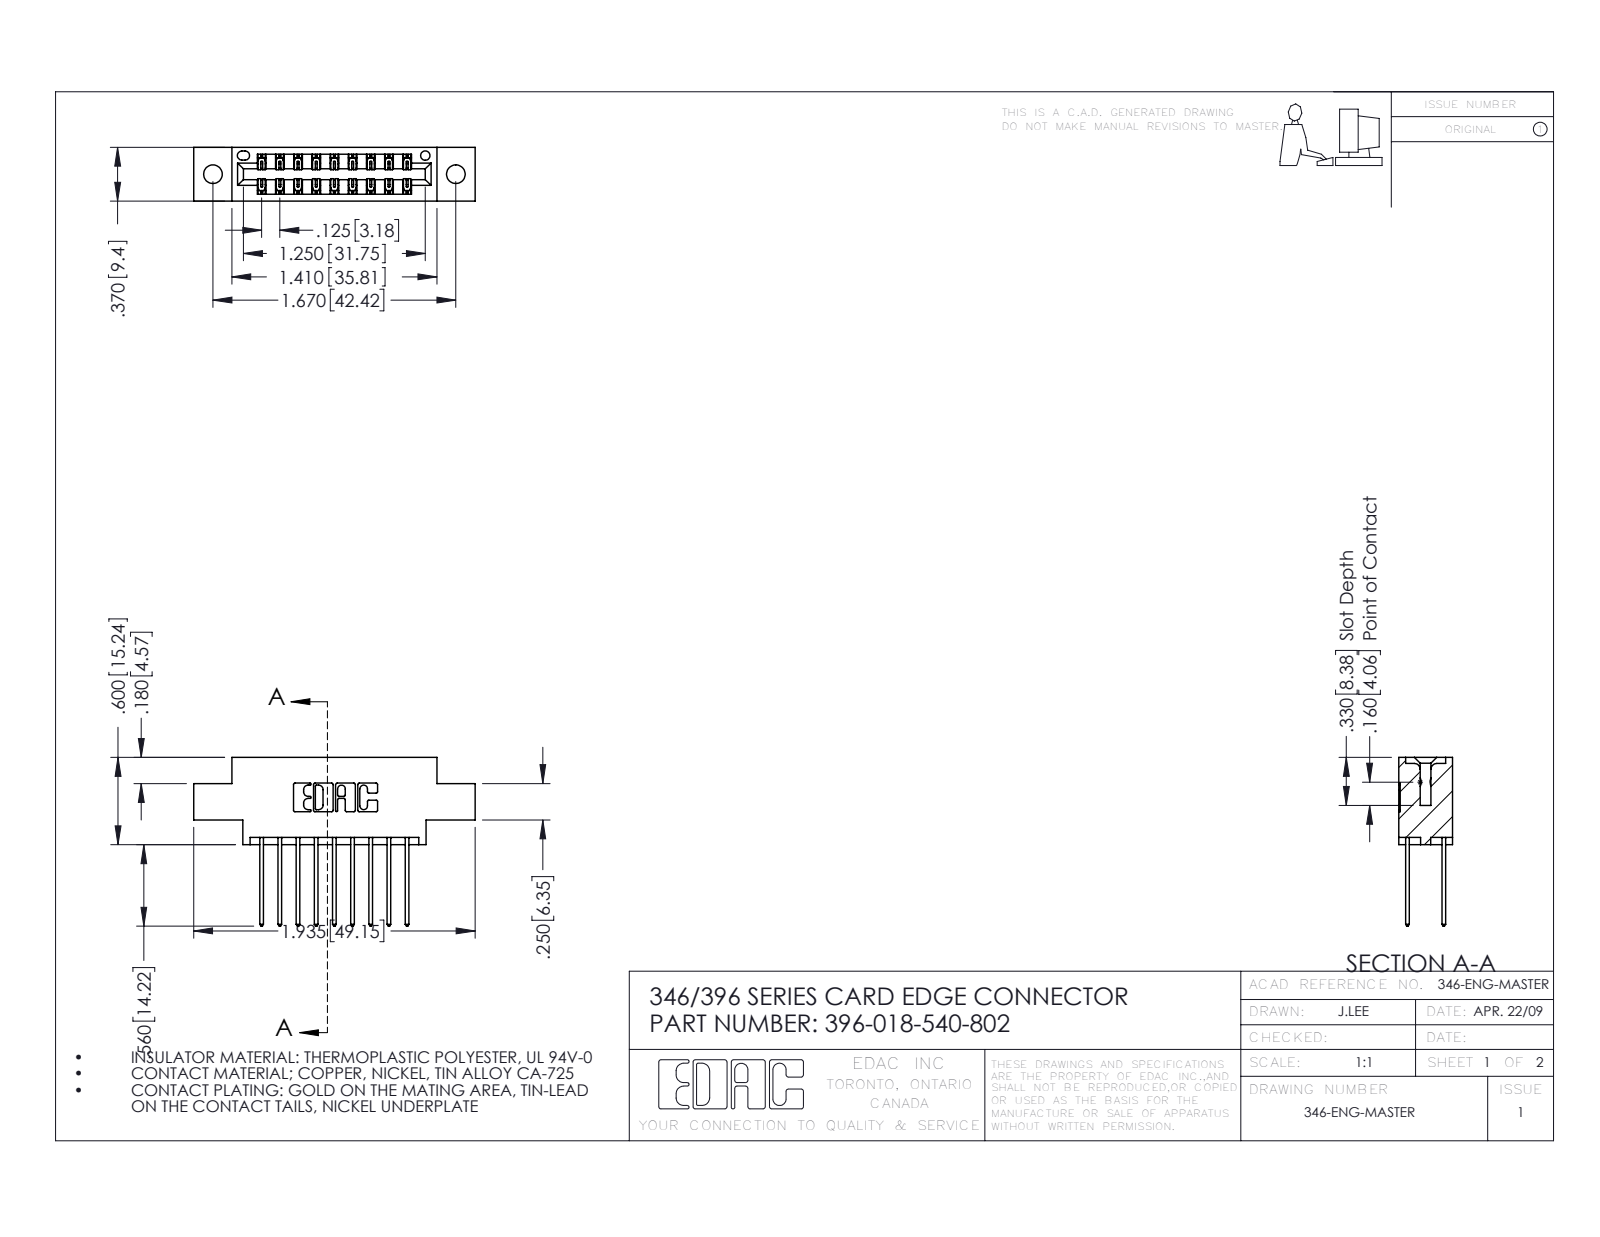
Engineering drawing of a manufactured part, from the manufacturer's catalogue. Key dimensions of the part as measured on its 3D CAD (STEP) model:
Part name (STEP PRODUCT): 396-018-540-802; 345-292-001_345-293-140; 346 Part_0.170 Offset - 0.128 Dia
STEP written by: SolidWorks 2016 (CONFIG_CONTROL_DESIGN)
Units: inches
Bodies: 19 solids, 1062 faces (710 planar, 352 cylindrical, 0 other)
Overall size (bounding box): 1.935 × 1.16 × 0.37
Volume: 0.269 in³ · Surface area: 8.96 in²
Round holes (diameter × count): ⌀0.128 ×2, ⌀0.064 ×1
Partial cylindrical surfaces — rounded edges, fillets, slot ends (radius × count): R0.006 ×27, R0.01 ×22, R0.01 ×18, R0.007 ×6, R0.031 ×6, R0.026 ×3, R0.014 ×2, R0.022 ×2
Main face-to-face distances: 0.25, 0.048, 0.322, 0.37, 0.072, 0.298, 0.025, 0.275, 0.225, 0.148
Hole centre spacings: 0.246, 1.465, 1.67
